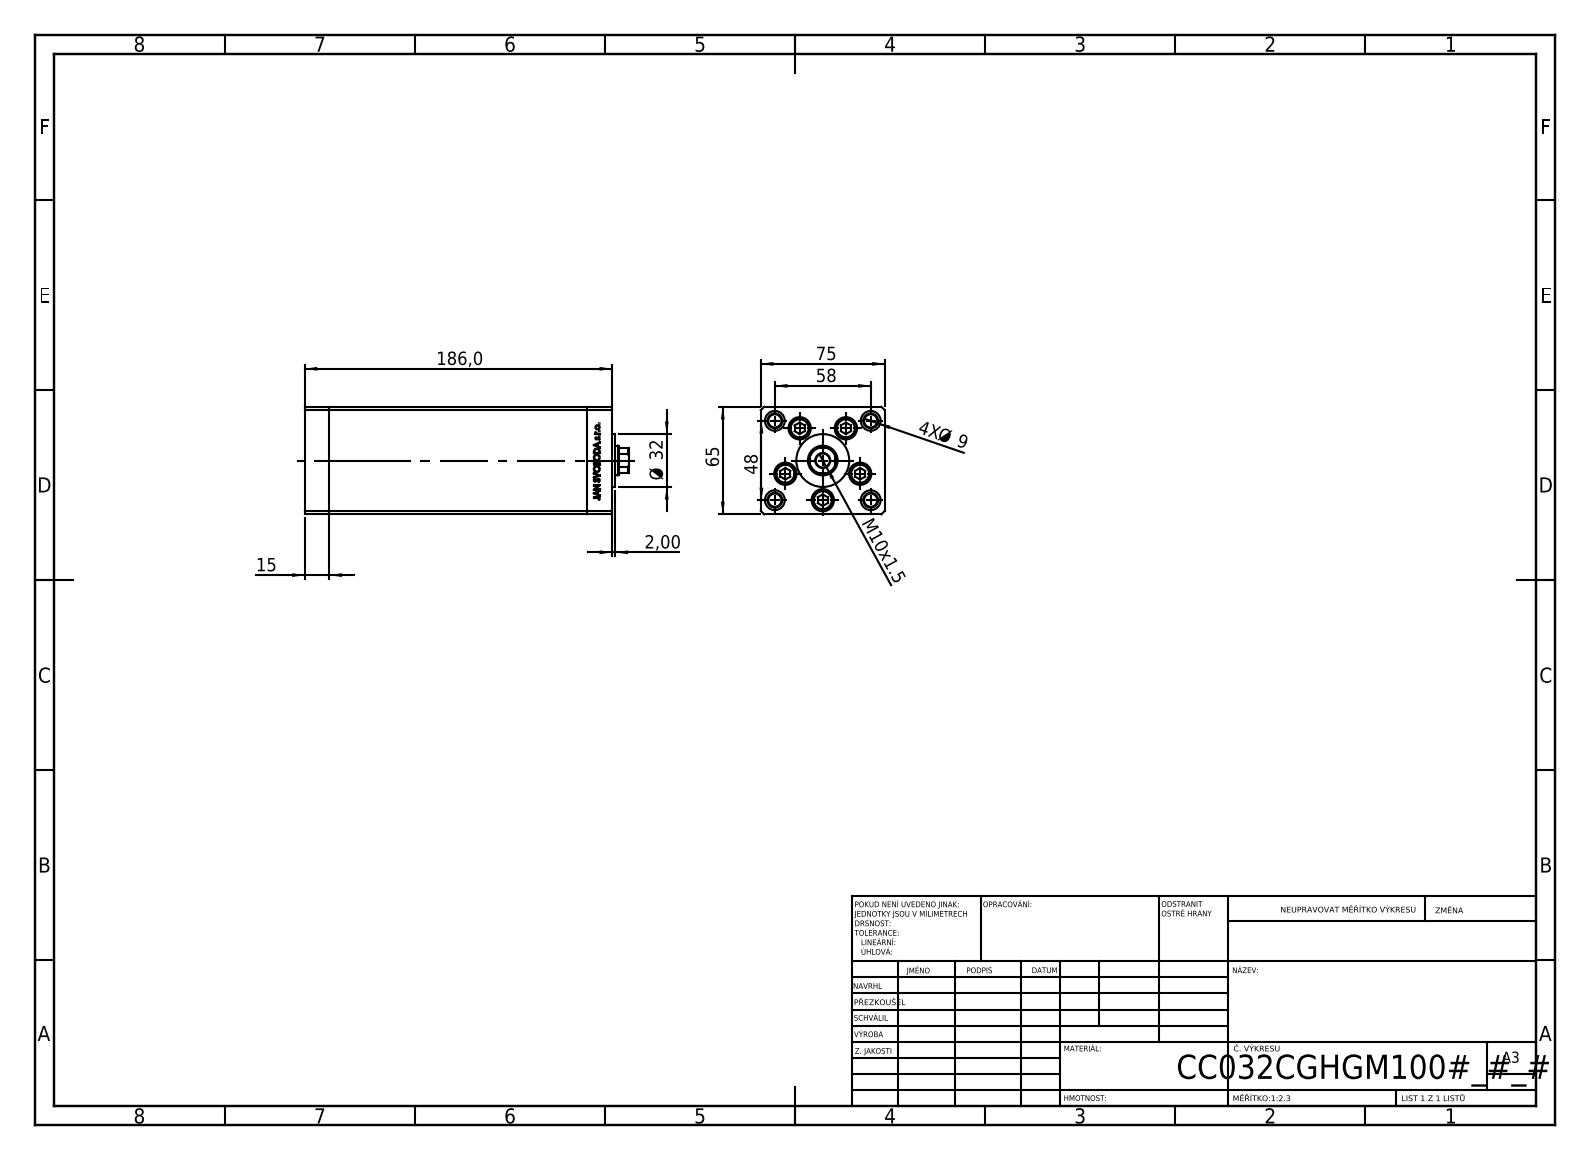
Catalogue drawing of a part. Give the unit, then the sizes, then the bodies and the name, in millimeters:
Units: millimetres
Overall size (bounding box): 196 × 75 × 65
Round holes (diameter × count): ⌀9 ×9, ⌀13.5 ×5, ⌀2 ×4, ⌀8 ×4, ⌀12 ×4, ⌀13.16 ×4, ⌀8.5 ×1, ⌀12.5 ×1, ⌀18 ×1
Round bosses / shafts (diameter × count): ⌀8 ×5, ⌀12.5 ×4, ⌀32 ×1
Partial cylindrical surfaces — rounded edges, fillets, slot ends (radius × count): R0.93 ×2, R8.5 ×1
Main face-to-face distances: 75, 65, 15, 156, 171, 186, 28, 13, 54.5, 10.5
Hole centre spacings: 24, 37.64, 15.67, 17.22, 27.71, 28.83, 29, 32.63
Volume: 754 279 mm³ · Surface area: 155 117 mm²
Bodies: 13 solids, 1179 faces (542 planar, 175 cylindrical, 462 other)
Part name (STEP PRODUCT): V220C BACK_C; V220C_C MIDDLE; V220C FRONT; V220C_VC_C (+1 more)
STEP written by: SolidWorks 2019 (CONFIG_CONTROL_DESIGN)
